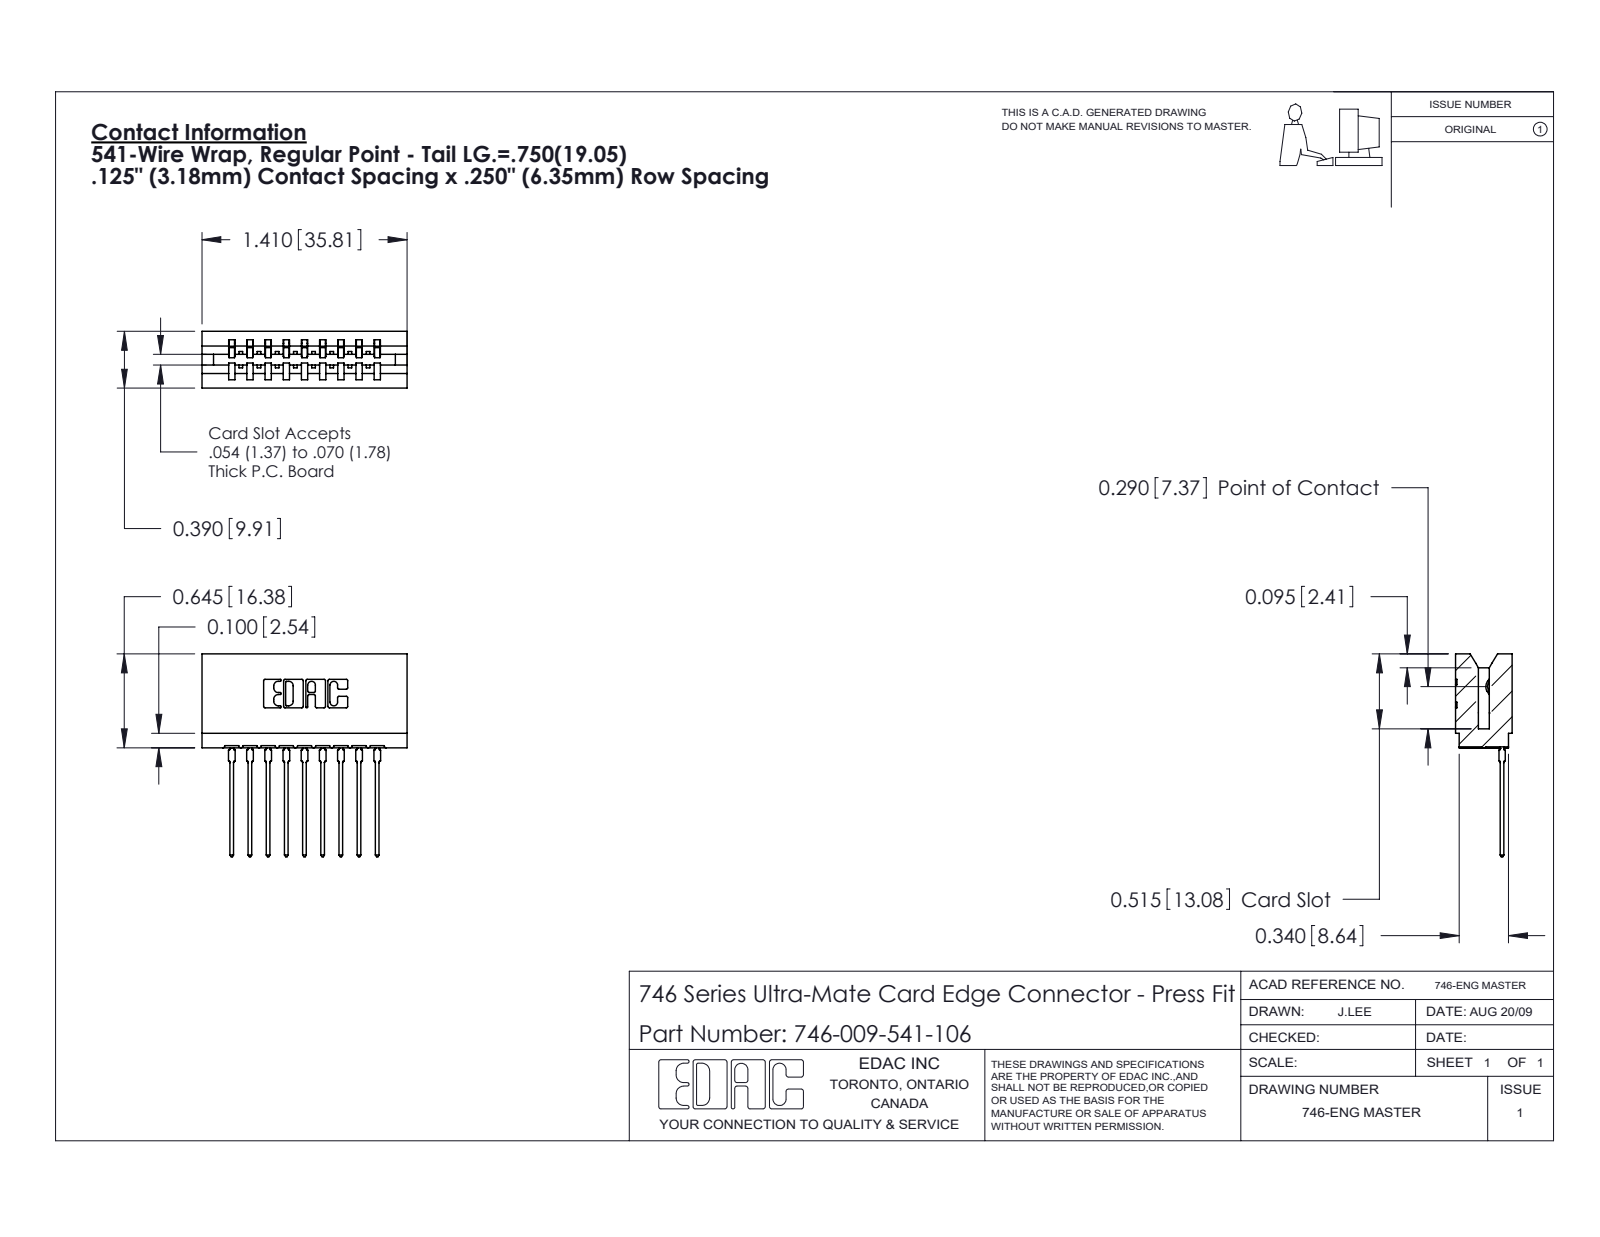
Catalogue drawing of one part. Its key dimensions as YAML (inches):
part_name: "746-292-001_541; 746 Part_.515 Slot Depth - 06; 746-009-541-106"
step_written_by: "SolidWorks 2020 (CONFIG_CONTROL_DESIGN)"
units: inches
bodies: {solids: 10, faces: 1070, planar: 623, cylindrical: 213, other: 234}
overall_size: [1.41, 1.394, 0.39]
volume: 0.243
surface_area: 8.66
partial_cylinders:
  - {radius: 0.01, count: 22}
  - {radius: 0.021, count: 18}
  - {radius: 0.015, count: 10}
  - {radius: 0.007, count: 6}
  - {radius: 0.031, count: 6}
  - {radius: 0.005, count: 4}
  - {radius: 0.011, count: 4}
  - {radius: 0.026, count: 3}
face_to_face_distances: [0.25, 0.5, 0.333, 0.042, 0.125, 0.125, 0.057, 0.292, 0.208, 0.083]
